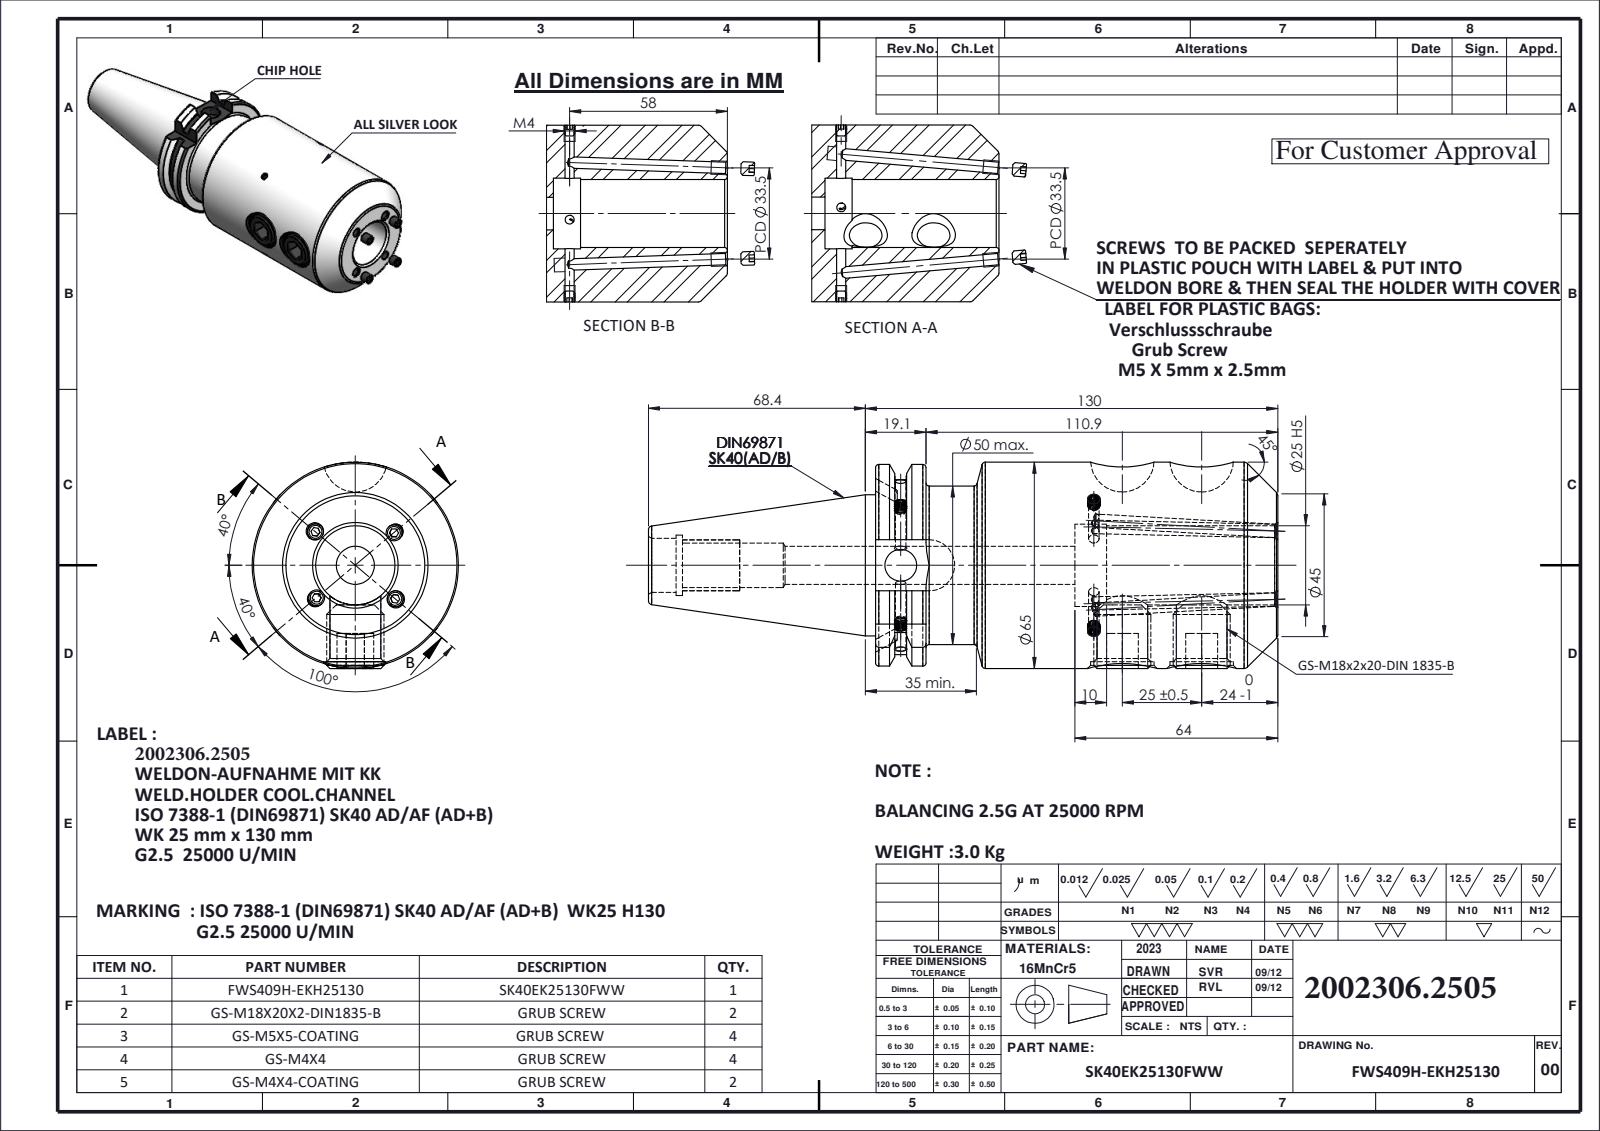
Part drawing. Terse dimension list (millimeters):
name: GS-M4X4-COATING_DIN 913 - M4 x 4-N; SK40EK25130FWW; GS-M18X20X2-DIN1835-B; GS-M4X4_DIN 913 - M4 x 4-N (+2 more)
written by: SolidWorks 2023 (CONFIG_CONTROL_DESIGN)
unit: mm
bodies: 13 solids, 545 faces (141 planar, 138 cylindrical, 266 other)
size: 208.56 × 65 × 65
volume: 390 930 mm³; area: 60 863 mm²
holes: 5× ⌀3.3, 4× ⌀4.2, 2× ⌀16, 2× ⌀20, 1× ⌀10, 1× ⌀12, 1× ⌀14, 1× ⌀17, 1× ⌀19, 1× ⌀25, 1× ⌀26
bosses: 6× ⌀4, 4× ⌀5, 2× ⌀18, 1× ⌀65, 1× ⌀50, 1× ⌀44.45
rounds: 1× R8.05, 1× R28.12, 1× R31.77
face distances: 126.8, 15.9, 110.9, 10, 62.8, 46.9, 64, 20, 12.5, 47.8
hole spacings: 25
